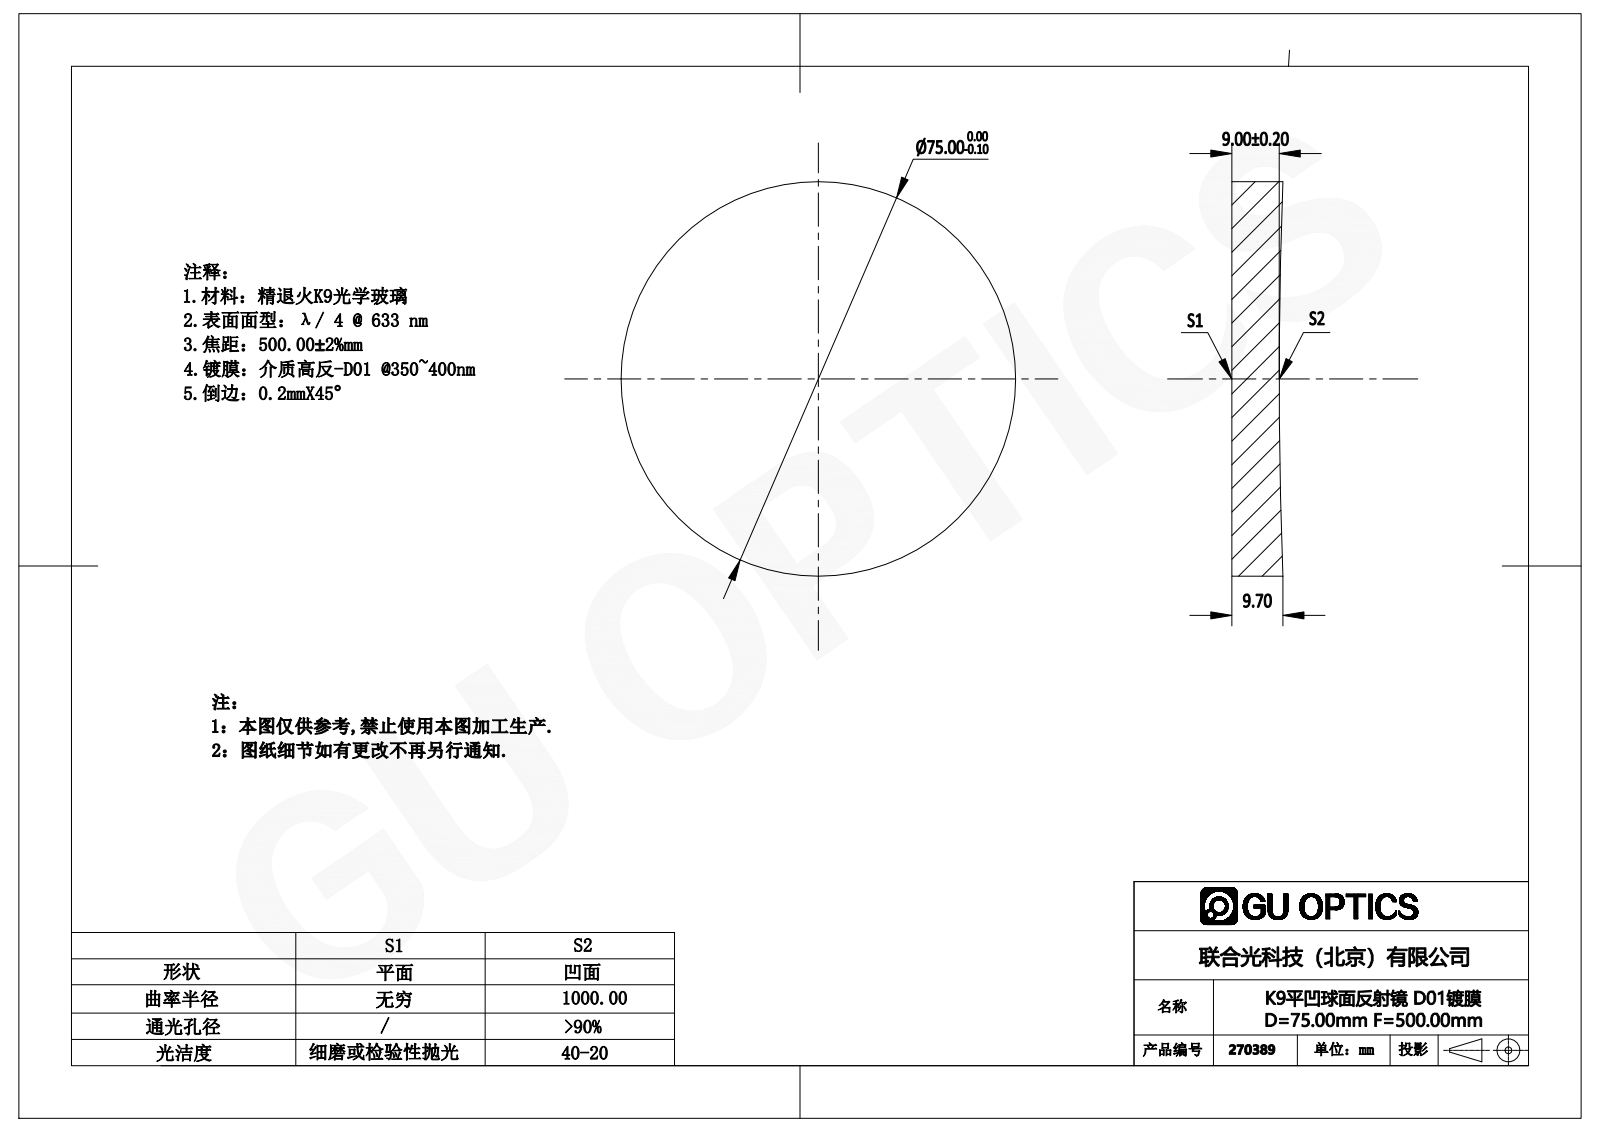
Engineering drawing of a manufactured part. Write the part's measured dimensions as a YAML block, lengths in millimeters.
part_name: "270064"
step_written_by: "SolidWorks 2016 (AUTOMOTIVE_DESIGN)"
units: millimeters
bodies: {solids: 1, faces: 5, planar: 1, cylindrical: 2, other: 2}
overall_size: [75, 75, 9.7]
volume: 41314
surface_area: 11124
round_bosses_or_shafts:
  - {diameter: 75, count: 1}
